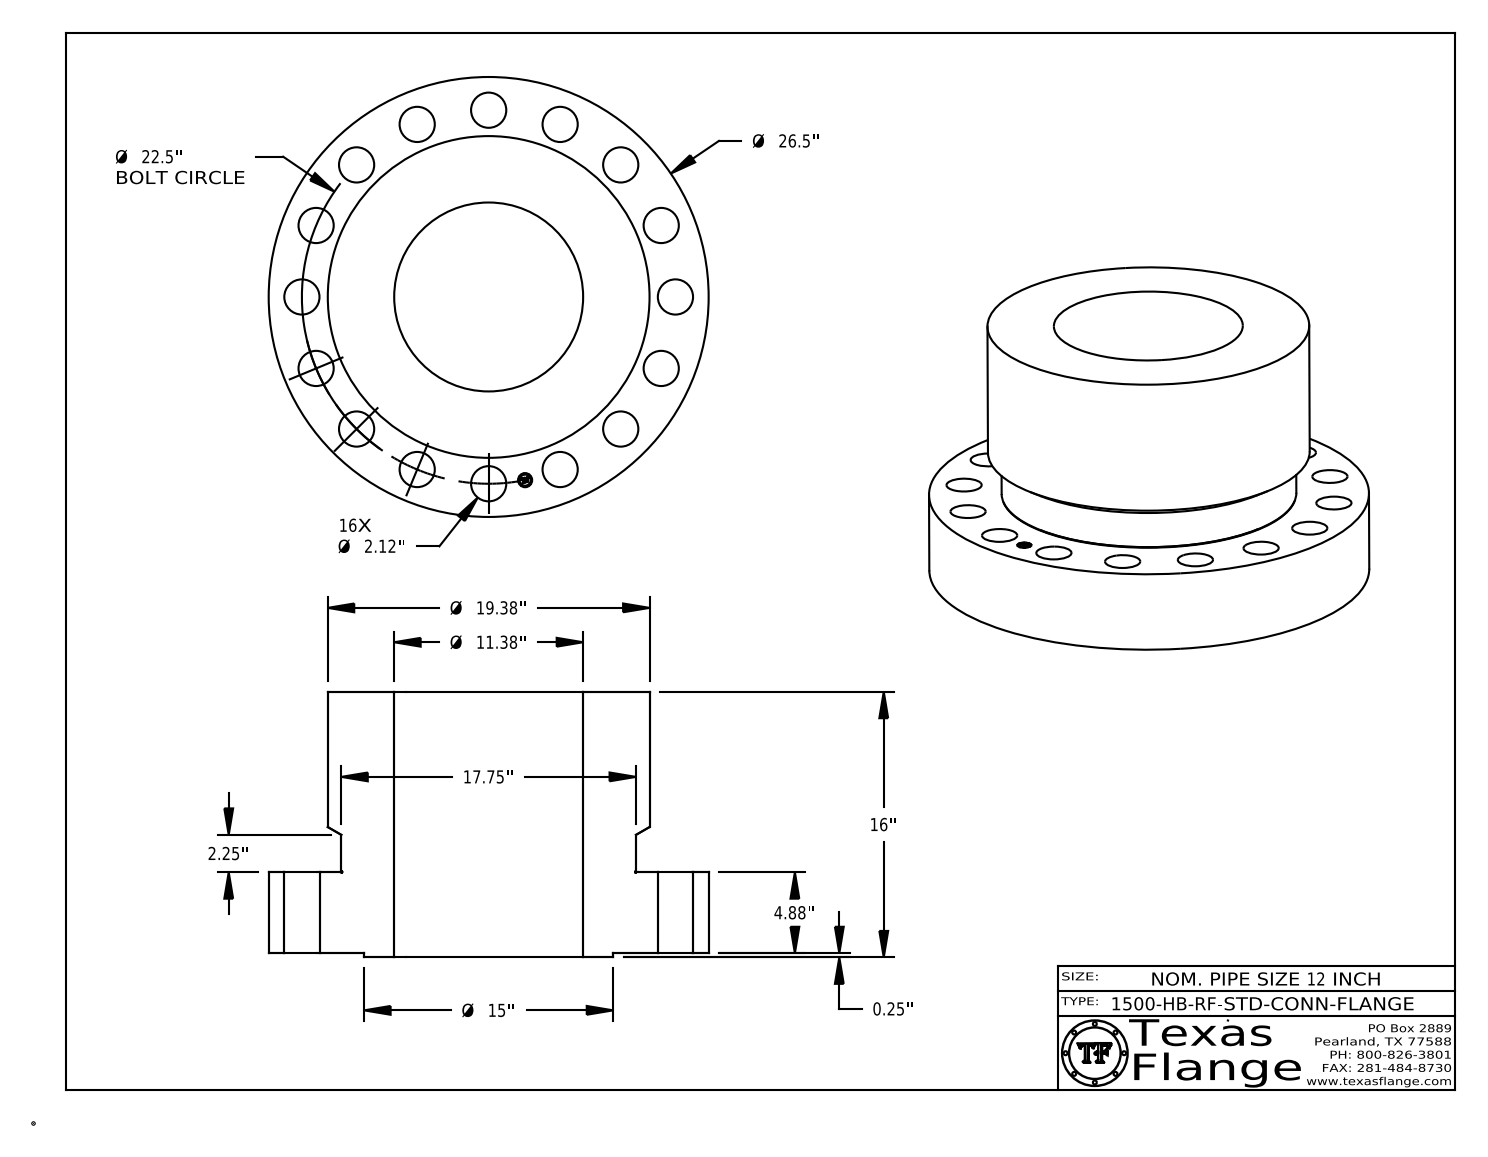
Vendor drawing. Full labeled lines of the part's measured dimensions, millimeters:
Part name (STEP PRODUCT): 12-1500-HB-RF-STD-CONN-FLANGE
STEP written by: CATIA V5 STEP AP214 (AUTOMOTIVE_DESIGN)
Units: millimetres
Bodies: 1 solid, 437 faces (369 planar, 62 cylindrical, 6 other)
Overall size (bounding box): 673.1 × 673.1 × 406.4
Volume: 64 250 000 mm³ · Surface area: 1 950 000 mm²
Round holes (diameter × count): ⌀53.8 ×16, ⌀21.6 ×1, ⌀289.1 ×1
Round bosses / shafts (diameter × count): ⌀1.3 ×8, ⌀673.1 ×1, ⌀492.3 ×1, ⌀450.9 ×1, ⌀381 ×1, ⌀17 ×1
Main face-to-face distances: 124, 400.1, 276.1, 6.4, 130.3, 406.4, 130.2, 123.8, 276.2, 0.4
Hole centre spacings: 317.5, 528, 560.5, 285.8, 218.7, 404.1, 111.5, 111.5
